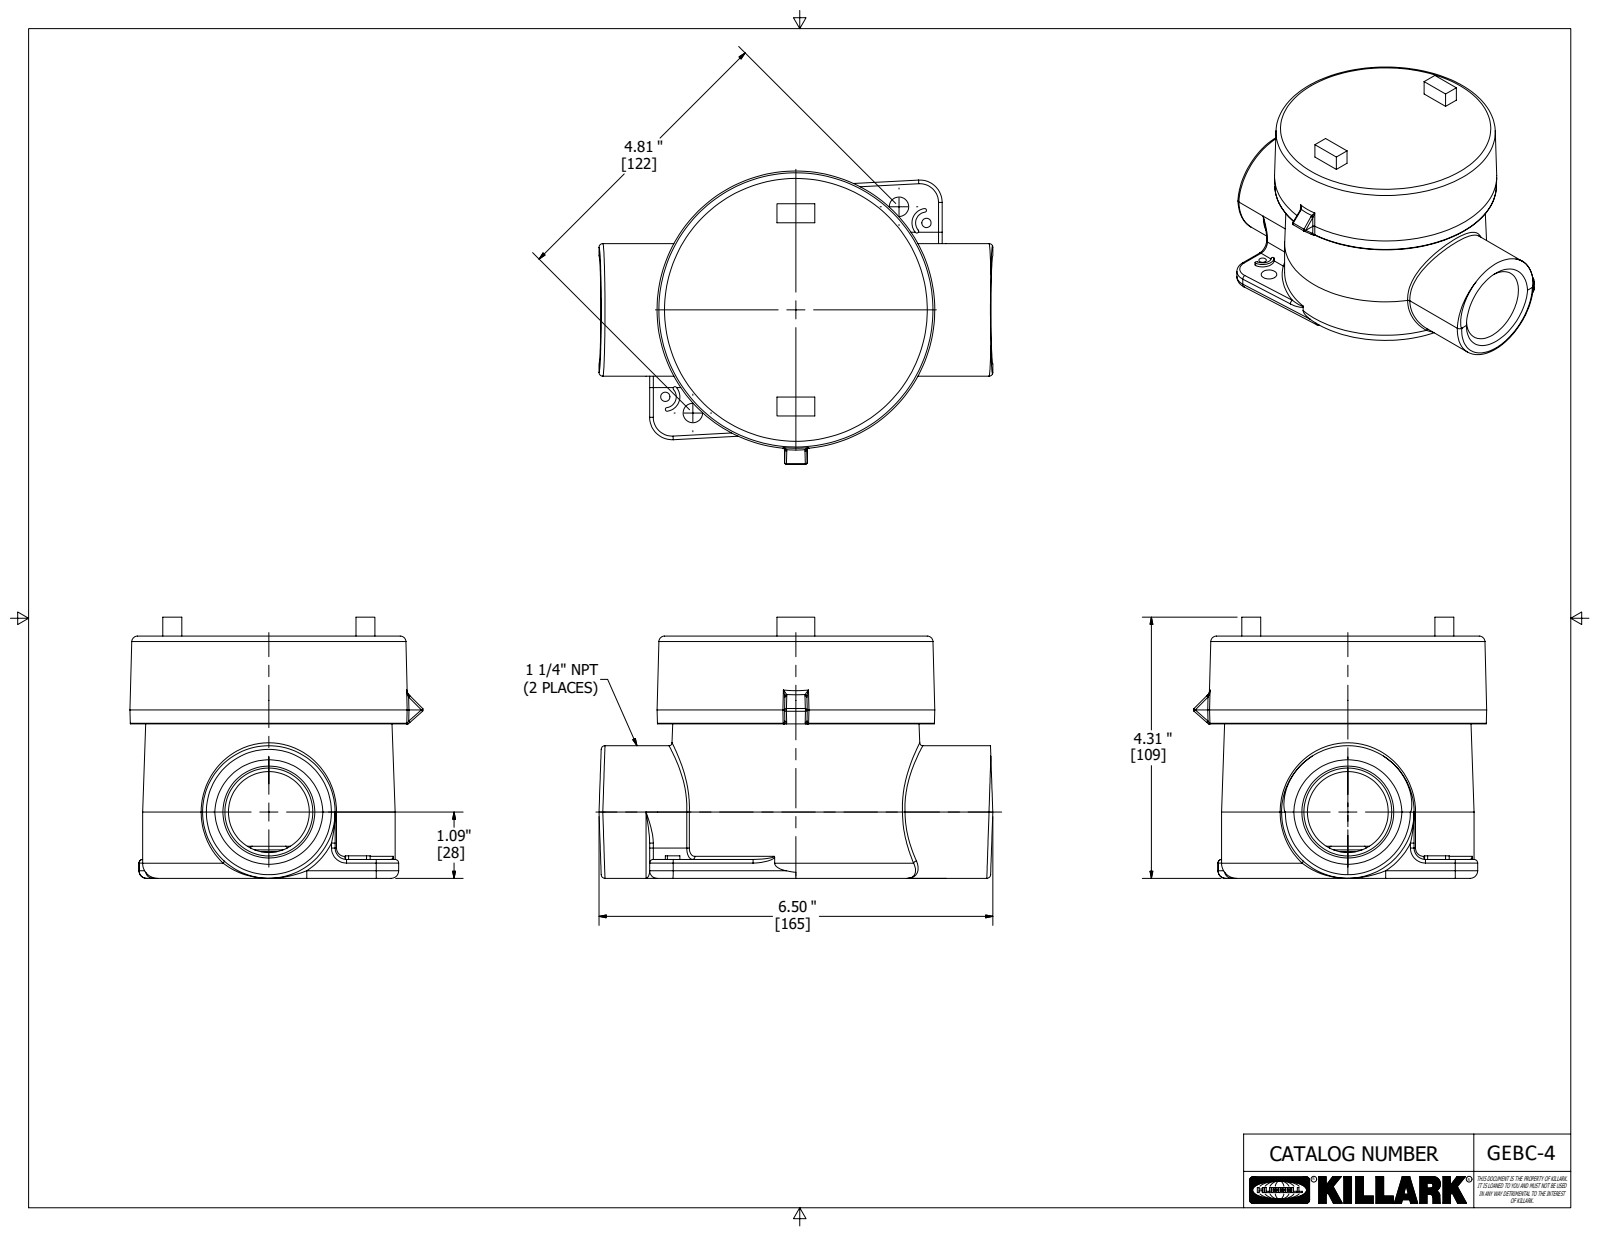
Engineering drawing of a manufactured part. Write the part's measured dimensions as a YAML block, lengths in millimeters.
part_name: "GEBC-4; 21161; 21147-override"
step_written_by: "Autodesk Inventor 2020 (AUTOMOTIVE_DESIGN)"
units: millimeters
bodies: {solids: 2, faces: 836, planar: 412, cylindrical: 91, other: 333}
overall_size: [165.1, 122.9, 109.5]
volume: 576300
surface_area: 129700
round_holes:
  - {diameter: 3.9, count: 2}
  - {diameter: 8.2, count: 2}
  - {diameter: 33.9, count: 1}
  - {diameter: 39.6, count: 1}
  - {diameter: 97.1, count: 1}
  - {diameter: 102.7, count: 1}
round_bosses_or_shafts:
  - {diameter: 55.6, count: 1}
partial_cylinders:
  - {radius: 1.5, count: 33}
  - {radius: 0.8, count: 14}
  - {radius: 3.2, count: 4}
  - {radius: 0.8, count: 3}
  - {radius: 1.3, count: 2}
  - {radius: 4.6, count: 2}
  - {radius: 4.7, count: 2}
  - {radius: 6.1, count: 2}
face_to_face_distances: [101.5, 90.4, 11.1, 64.7, 25.7, 36.8, 88.9, 9.7, 55.1, 80.8]
hole_center_spacings: [13.4, 126.2, 61.1, 61.1, 65.8, 65.8, 122.2, 131.5]
